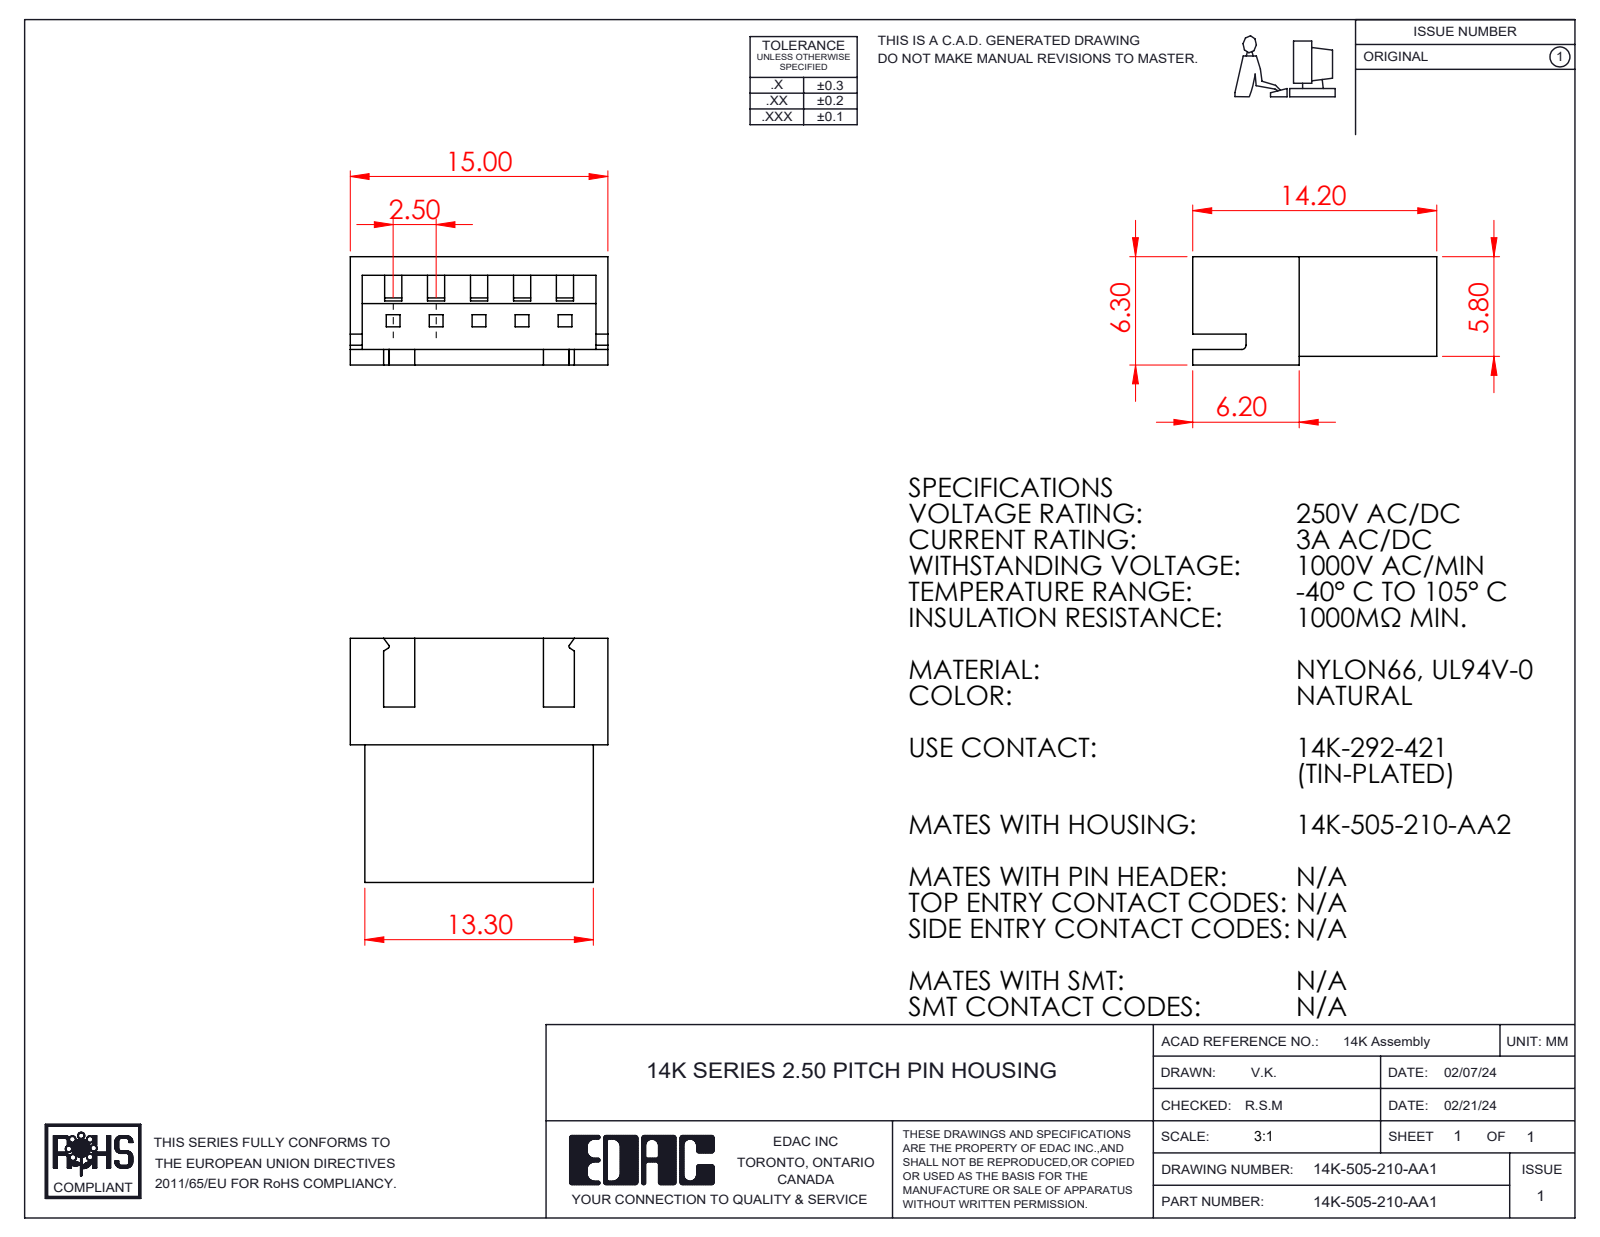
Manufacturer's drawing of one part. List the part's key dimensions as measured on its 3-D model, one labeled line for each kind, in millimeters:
Part name (STEP PRODUCT): 14K-505-210-AA1
STEP written by: SolidWorks 2023 (CONFIG_CONTROL_DESIGN)
Units: millimetres
Bodies: 1 solid, 164 faces (160 planar, 4 cylindrical, 0 other)
Overall size (bounding box): 15 × 14.2 × 6.3
Volume: 636 mm³ · Surface area: 1 472 mm²
Partial cylindrical surfaces — rounded edges, fillets, slot ends (radius × count): R0.1 ×2, R0.25 ×1
Main face-to-face distances: 0.5, 2.5, 5, 5.8, 0.9, 3, 2, 4.5, 1.5, 7.5
